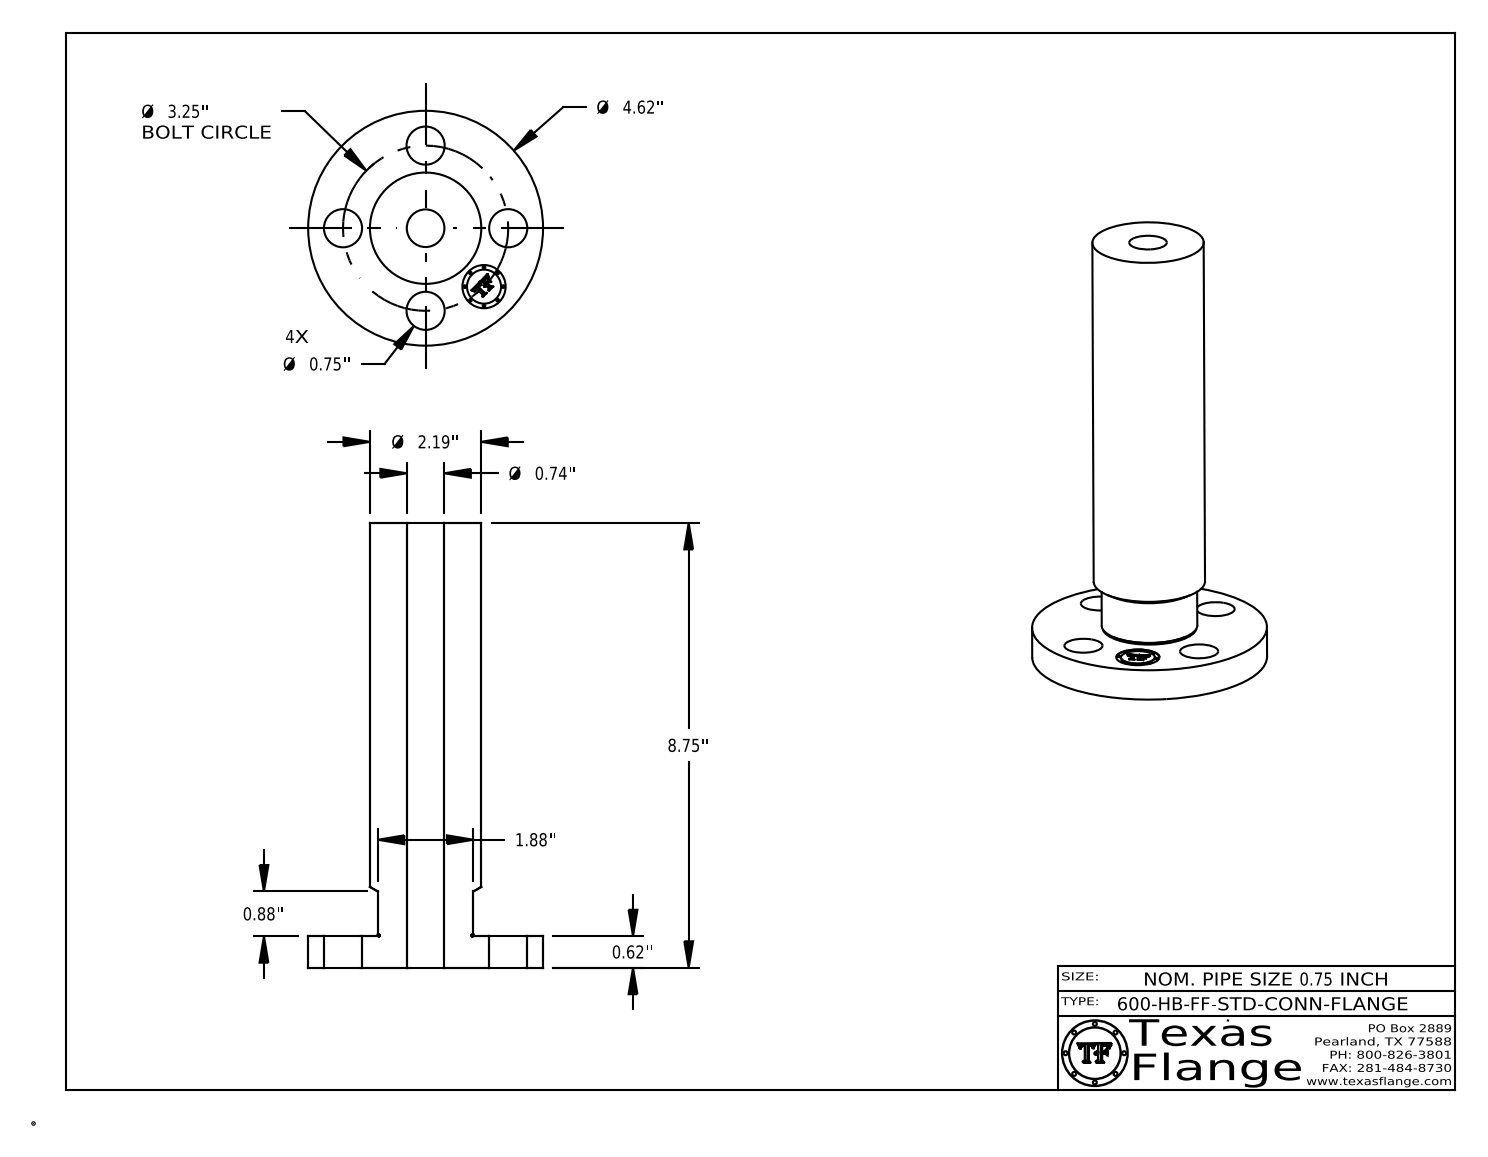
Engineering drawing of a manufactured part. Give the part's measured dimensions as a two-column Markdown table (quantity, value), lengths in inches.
| quantity | value |
| --- | --- |
| part name | 0.75-600-HB-FF-STD-CONN-FLANGE |
| STEP written by | CATIA V5 STEP AP214 (AUTOMOTIVE_DESIGN) |
| units | inches |
| bodies | 1 solid, 410 faces (368 planar, 36 cylindrical, 6 other) |
| overall size | 8.75 × 4.62 × 4.62 |
| volume | 35.24 in³ |
| surface area | 121.2 in² |
| round holes (diameter × count) | 0.75 × 4, 0.74 × 1, 0.85 × 1 |
| round bosses / shafts (diameter × count) | 0.051 × 8, 4.62 × 1, 2.19 × 1, 1.88 × 1, 0.67 × 1 |
| main face-to-face distances | 0.62, 8.75, 8.13, 0.615, 8.135, 0.254, 0.248, 0.016, 0.046, 0.165 |
| hole center spacings | 1.625, 2.298, 1.244, 3.003, 3.25 |
